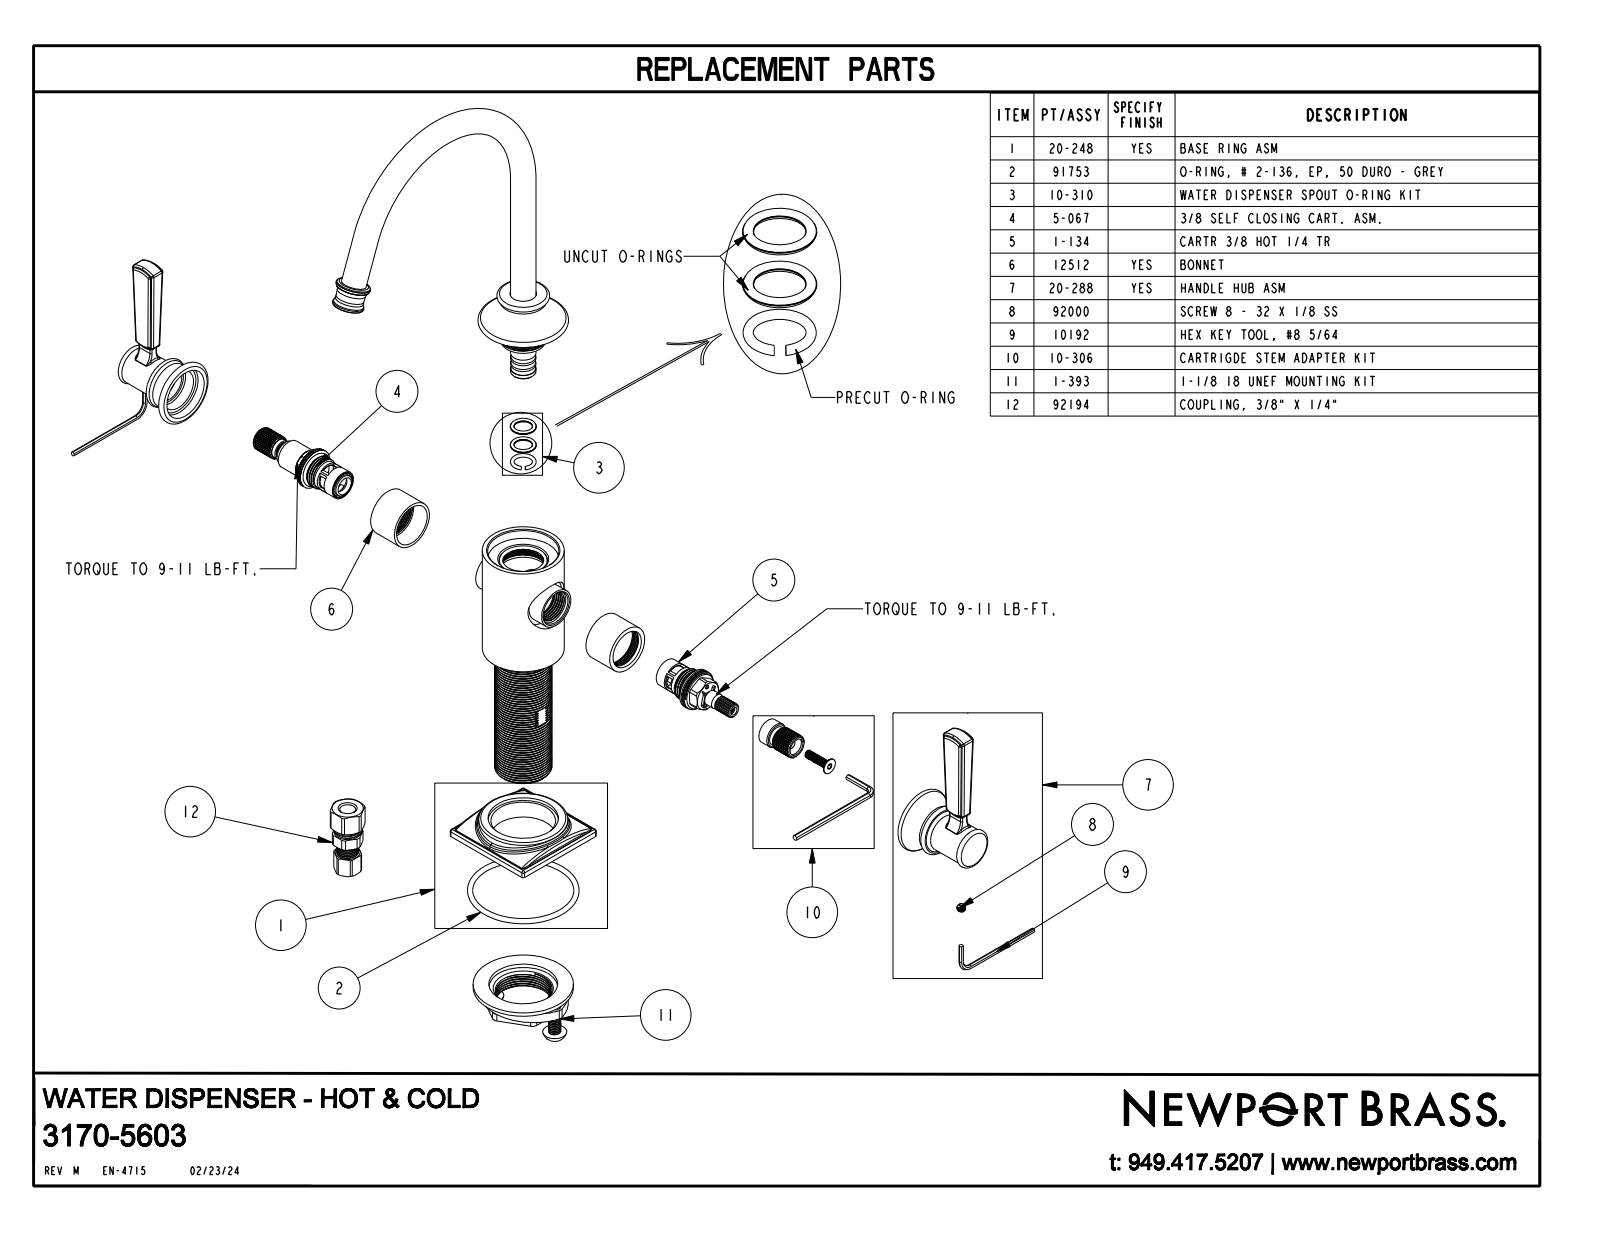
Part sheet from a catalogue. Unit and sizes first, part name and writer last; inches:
Units: inches
Overall size (bounding box): 9.425 × 6.053 × 5.125
Round holes (diameter × count): ⌀1 ×1
Round bosses / shafts (diameter × count): ⌀0.5 ×2, ⌀1.75 ×1, ⌀1.61 ×1, ⌀0.97 ×1, ⌀0.76 ×1
Partial cylindrical surfaces — rounded edges, fillets, slot ends (radius × count): R0.04 ×24, R0.02 ×16, R0.03 ×10, R0.037 ×8, R0.33 ×2, R0.45 ×2, R0.57 ×2
Main face-to-face distances: 4.245, 3.47, 2.05, 5.125, 3.635, 1.49, 1.49, 2.145, 3.635, 1.535
Volume: 12.26 in³ · Surface area: 63.34 in²
Bodies: 1 solid, 379 faces (37 planar, 92 cylindrical, 250 other)
Part name (STEP PRODUCT): 3170-5603
STEP written by: CREO PARAMETRIC BY PTC INC, 2018400 (CONFIG_CONTROL_DESIGN)
